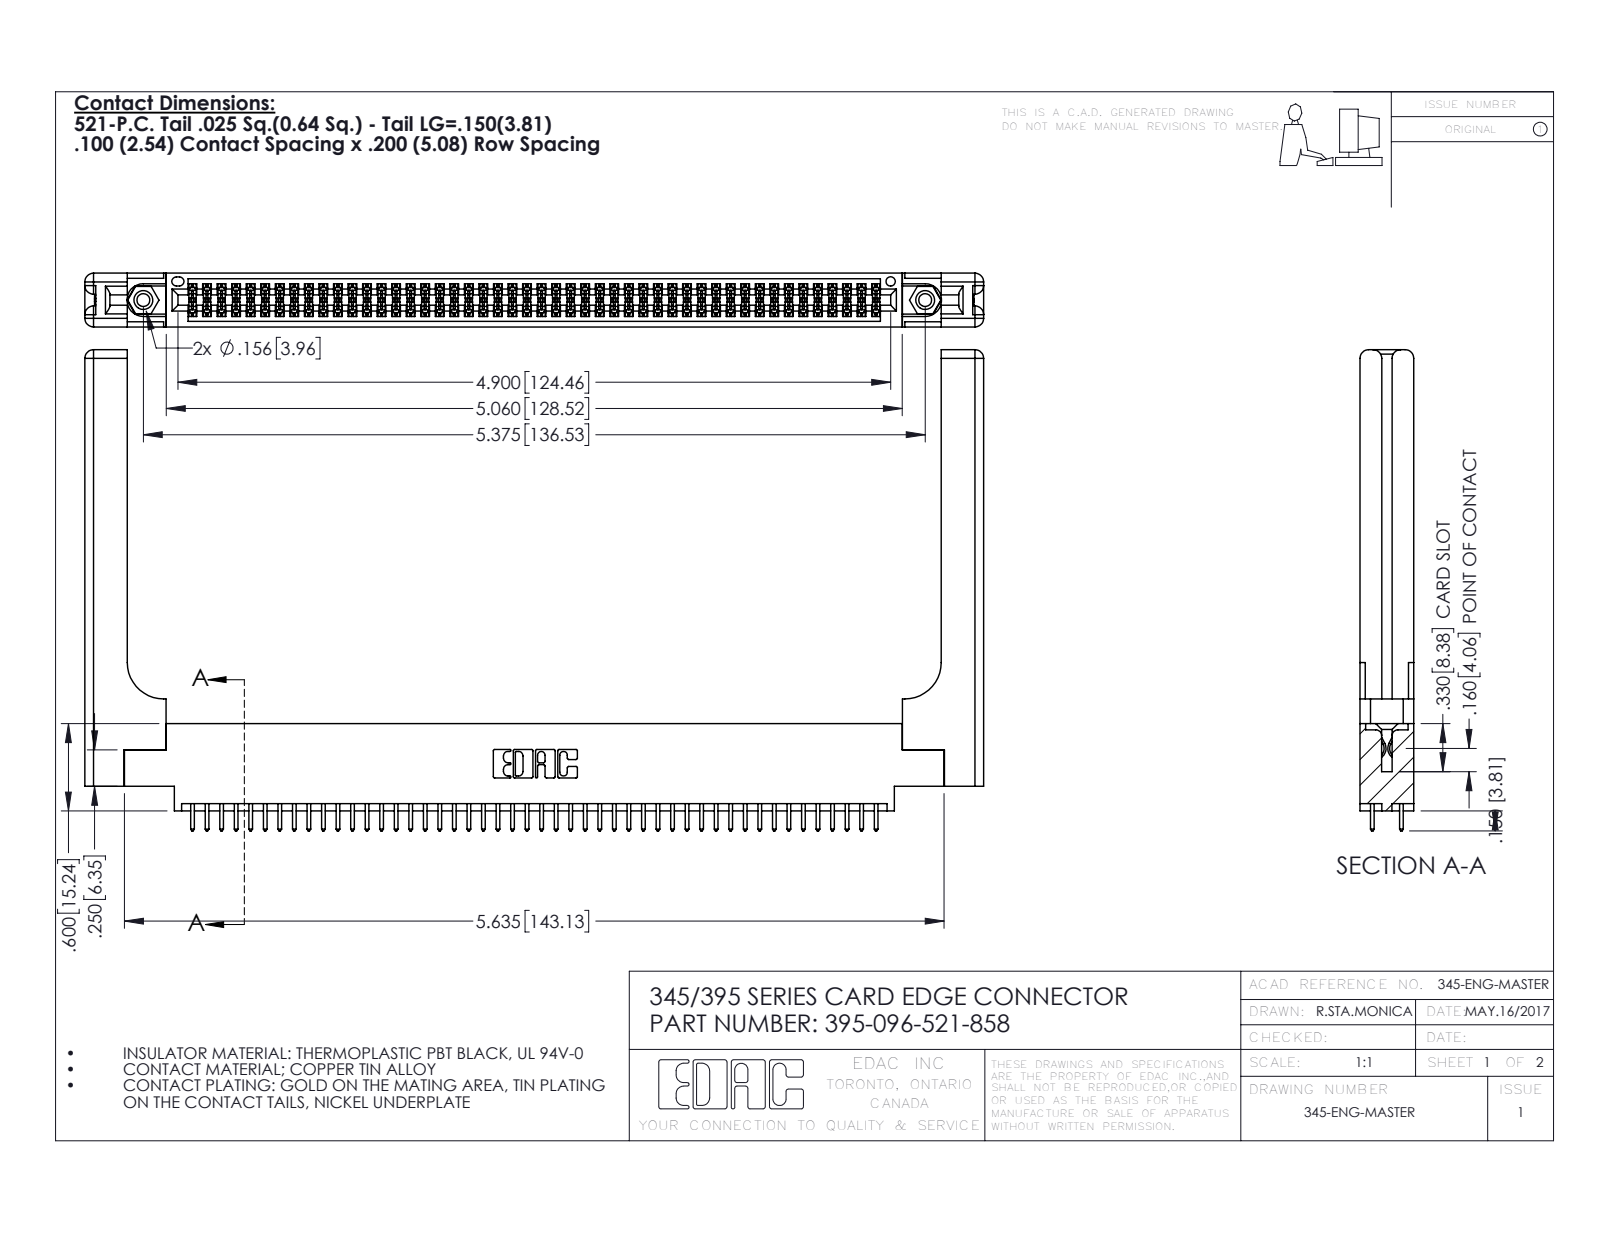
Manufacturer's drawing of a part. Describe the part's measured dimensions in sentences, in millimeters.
The part is named "345-292-001_345-293-121; 345-250-001_345-250-001-102; 345-220-058_345-220-058; 345 Part_0.170 Offset - 0.156 Dia-TH (+1 more)". Its 3-D file was written by "SolidWorks 2016 (CONFIG_CONTROL_DESIGN)". It is 101 solids with 5186 faces: 3400 planar, 1726 cylindrical and 60 other. Overall it measures 156.9 by 84 by 9.4 millimeters. Its volume is 23 630 cubic millimeters and its surface area 27 460 square millimeters. Round holes: 2 of diameter 2.3, 2 of diameter 3.2, 2 of diameter 4, 1 of diameter 1.6. Round bosses or shafts: 2 of diameter 3.9. Partial cylindrical surfaces (rounded edges, fillets, slot ends): 144 of radius 0.2, 96 of radius 0.3, 22 of radius 0.3, 16 of radius 1.5, 6 of radius 0.2, 6 of radius 0.8, 3 of radius 0.7, 2 of radius 0.4. The main face-to-face distances are 1.8, 7.6, 9.4, 2.5, 6.9, 0.6, 5.1, 5.7, 4.4, 3.8. The hole center spacings are 6.9, 130.5, 136.5.
